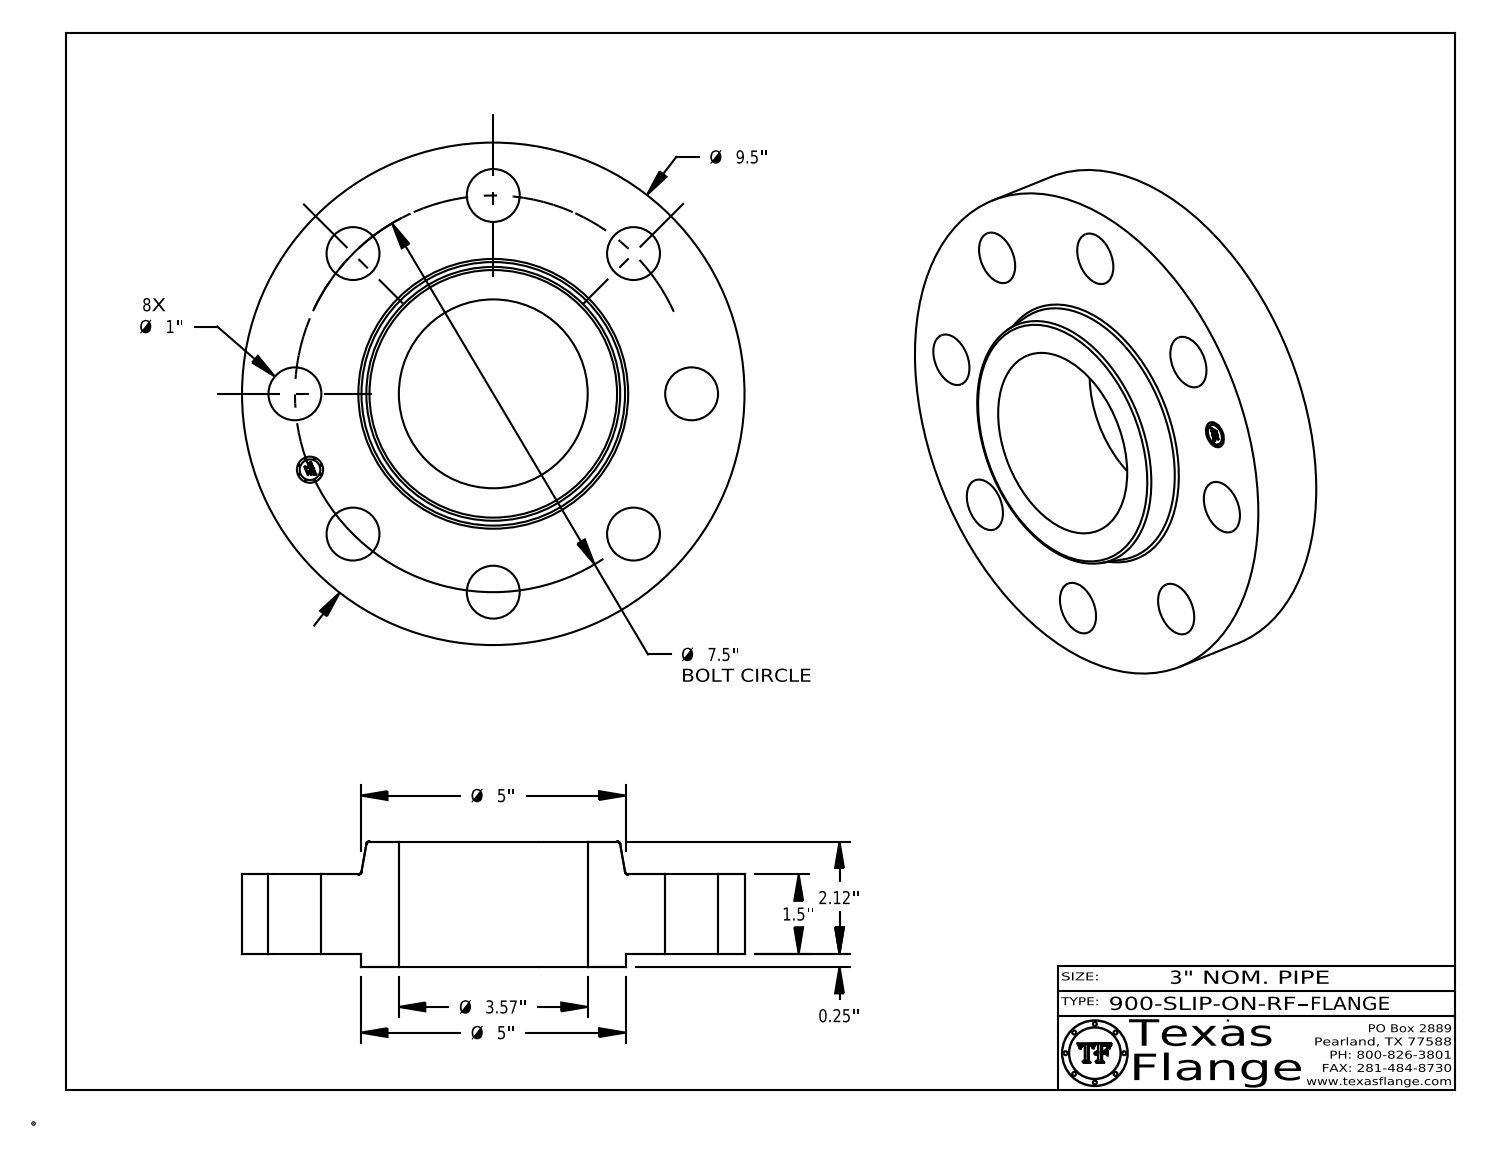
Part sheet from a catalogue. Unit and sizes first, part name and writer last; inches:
Units: inches
Overall size (bounding box): 9.5 × 9.5 × 2.37
Round holes (diameter × count): ⌀1 ×8, ⌀0.495 ×1, ⌀3.57 ×1
Round bosses / shafts (diameter × count): ⌀0.03 ×8, ⌀9.5 ×1, ⌀5 ×1, ⌀0.39 ×1
Main face-to-face distances: 1.5, 0.25, 1.75, 2.37, 2.12, 0.62, 0.015, 1.735, 1.485, 0.635
Hole centre spacings: 3.75, 2.87, 5.303, 6.929, 1.463, 6.236, 7.356, 7.5
Volume: 89.73 in³ · Surface area: 229.7 in²
Bodies: 1 solid, 417 faces (369 planar, 42 cylindrical, 6 other)
Part name (STEP PRODUCT): 900-SLIP-ON-RF
STEP written by: CATIA V5 STEP AP214 (AUTOMOTIVE_DESIGN)
